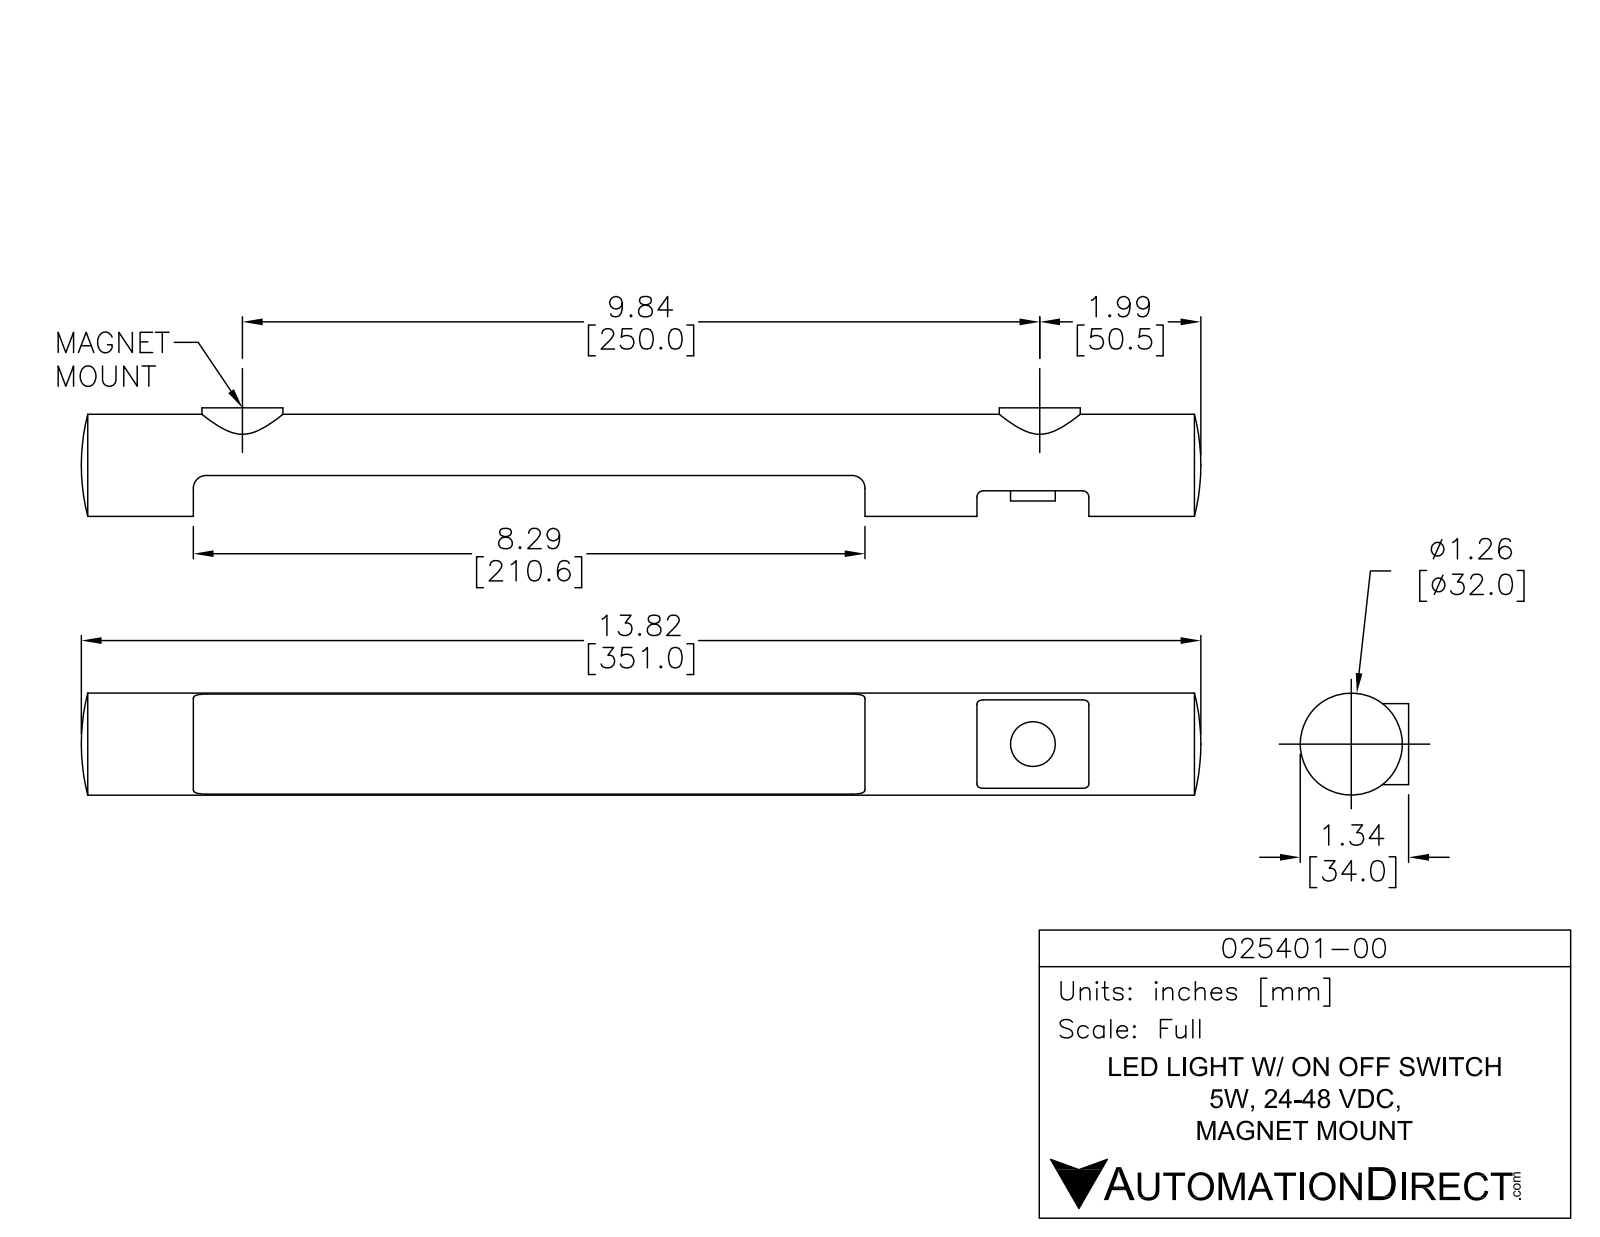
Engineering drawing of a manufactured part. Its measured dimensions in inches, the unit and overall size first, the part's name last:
Units: inches
Overall size (bounding box): 13.758 × 1.35 × 1.26
Round holes (diameter × count): ⌀0.077 ×2
Round bosses / shafts (diameter × count): ⌀0.985 ×2, ⌀0.073 ×2, ⌀1.26 ×1, ⌀0.865 ×1, ⌀0.865 ×1
Partial cylindrical surfaces — rounded edges, fillets, slot ends (radius × count): R0.06 ×4, R0.2 ×4, R0.12 ×2, R0.03 ×1, R1.209 ×1
Main face-to-face distances: 0.885, 0.03, 0.545, 0.22, 0.325, 0.53, 0.04, 0.845, 0.56, 0.03
Hole centre spacings: 0.2
Volume: 13.32 in³ · Surface area: 57.38 in²
Bodies: 1 solid, 138 faces (85 planar, 33 cylindrical, 20 other)
Part name (STEP PRODUCT): 025401-00
STEP written by: SolidWorks 2013 (AUTOMOTIVE_DESIGN)
